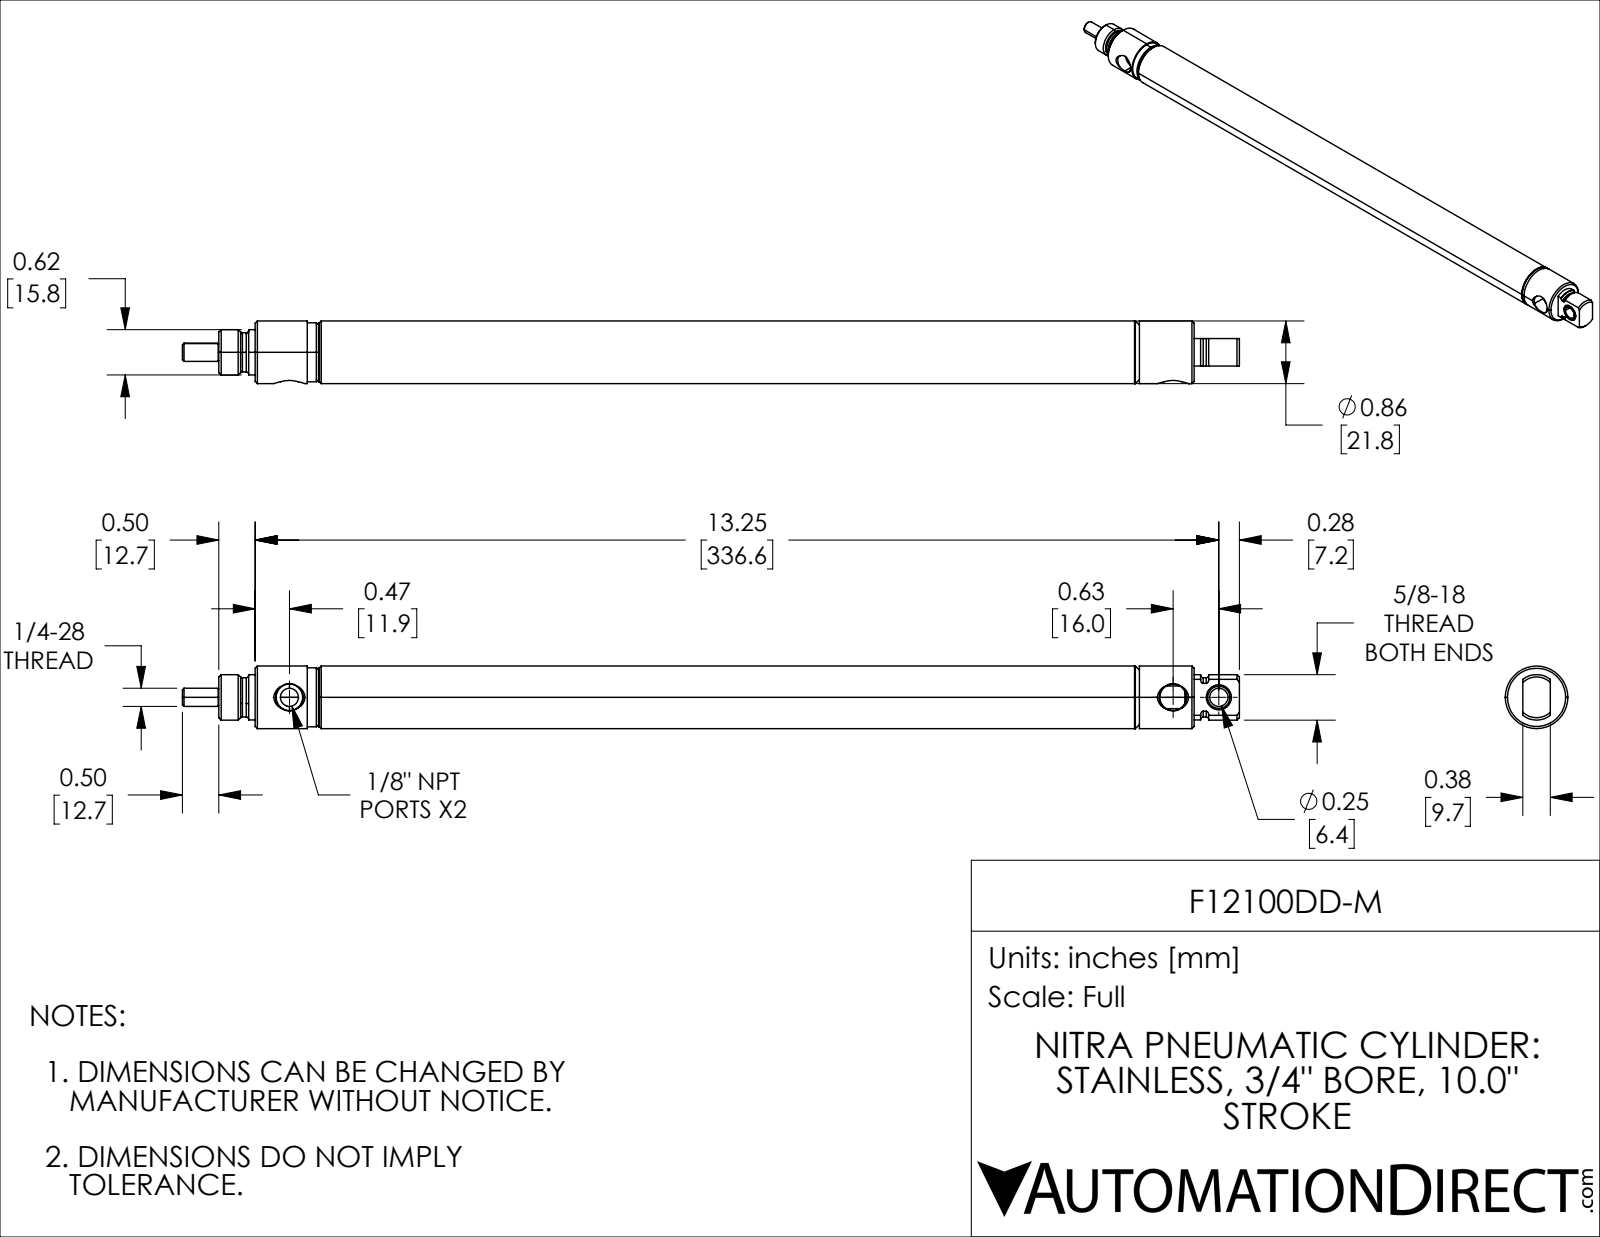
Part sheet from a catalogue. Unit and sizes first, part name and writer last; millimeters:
Units: millimetres
Overall size (bounding box): 369.11 × 21.84 × 21.84
Round holes (diameter × count): ⌀6.35 ×1, ⌀6.38 ×1, ⌀6.95 ×1, ⌀7.92 ×1, ⌀8.78 ×1, ⌀9.23 ×1, ⌀12.7 ×1, ⌀17.83 ×1
Round bosses / shafts (diameter × count): ⌀21.84 ×1, ⌀20.57 ×1, ⌀19.35 ×1, ⌀15.88 ×1, ⌀15.81 ×1, ⌀13.68 ×1, ⌀6.35 ×1, ⌀5.84 ×1
Partial cylindrical surfaces — rounded edges, fillets, slot ends (radius × count): R6.84 ×1
Main face-to-face distances: 21.43, 40.49, 315.92, 254, 275.43, 300.12, 46.12, 24.69, 12.7, 9.66
Hole centre spacings: 16, 308.61, 324.61
Volume: 57 788 mm³ · Surface area: 54 378 mm²
Bodies: 5 solids, 158 faces (29 planar, 61 cylindrical, 68 other)
Part name (STEP PRODUCT): F12100DD-M; F12100DD-M_9; F12100DD-M_3; F12100DD-M_5 (+2 more)
STEP written by: SolidWorks 2021 (CONFIG_CONTROL_DESIGN)
